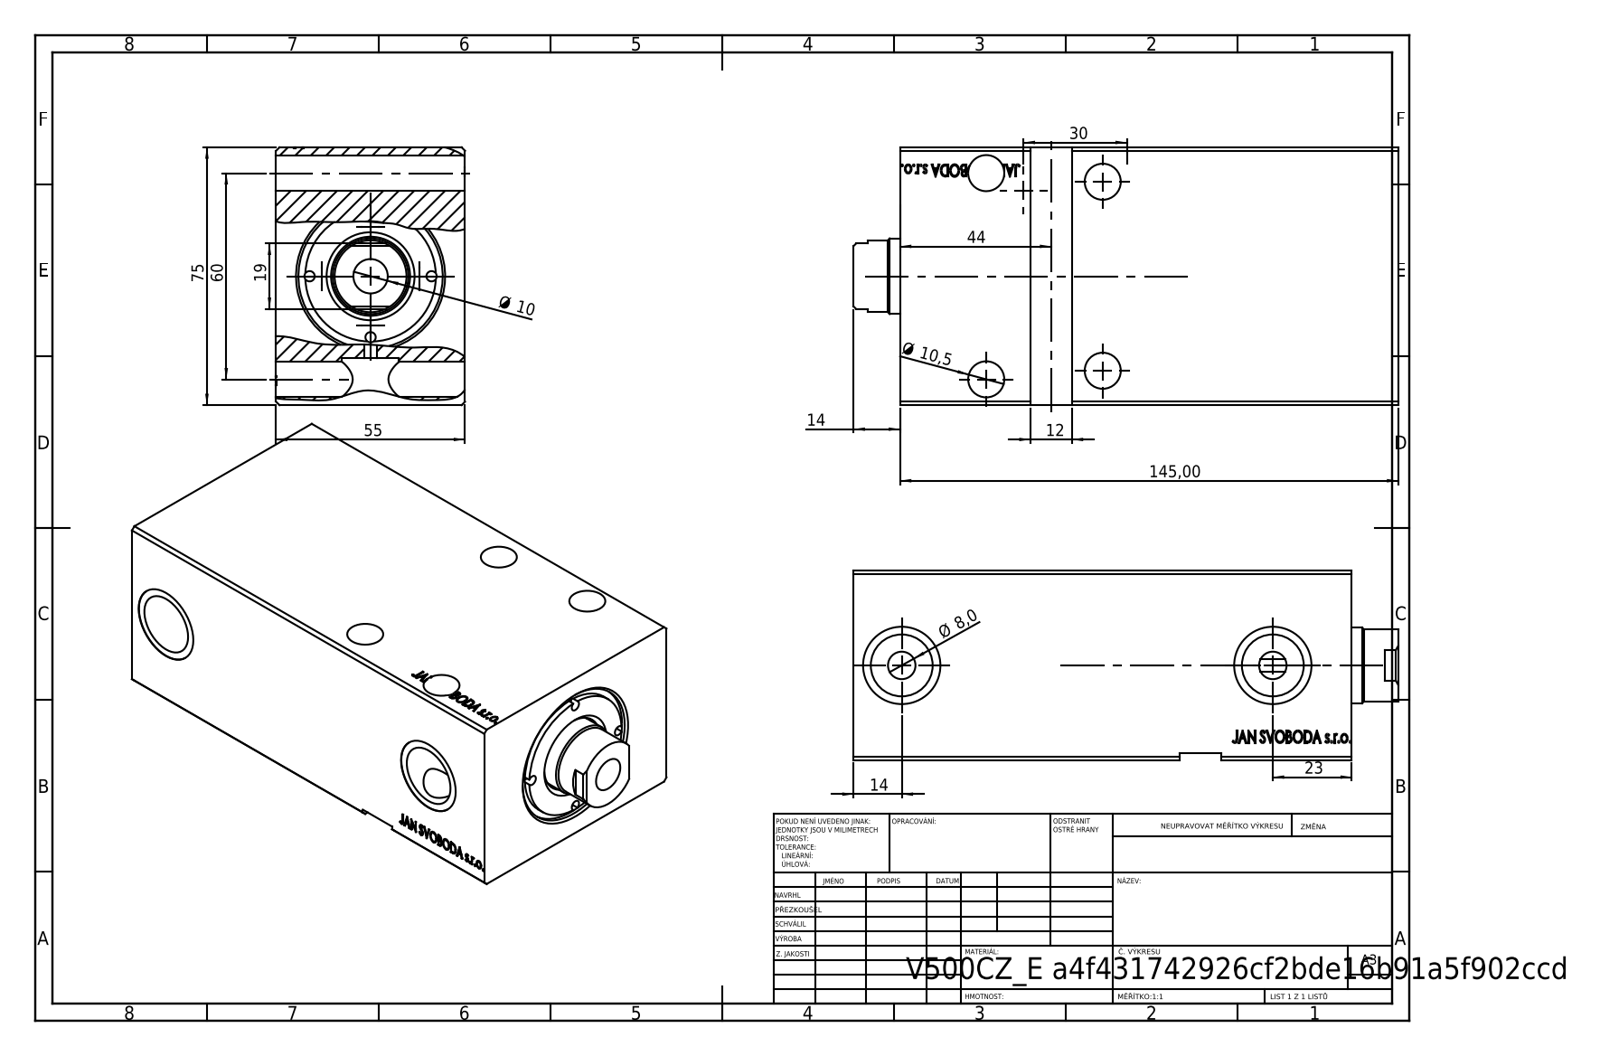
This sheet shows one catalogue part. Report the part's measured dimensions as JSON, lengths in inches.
{"part_name": "V500CZ_VCP_E; V500CZ_VC_vysunovaci_E; V500CZ_E", "step_written_by": "SolidWorks 2019 (CONFIG_CONTROL_DESIGN)", "units": "inches", "bodies": {"solids": 3, "faces": 782, "planar": 376, "cylindrical": 54, "other": 352}, "overall_size": [6.24, 2.953, 2.165], "volume_in3": 32.99, "surface_area_in2": 126.9, "round_holes": [[0.118, 4], [0.413, 4], [0.315, 2], [0.709, 2], [0.886, 2], [0.394, 1], [0.866, 1], [0.906, 1], [1.26, 1], [1.417, 1], [1.654, 1]], "round_bosses_or_shafts": [[1.496, 1], [0.824, 1]], "face_to_face_distances": [2.165, 2.953, 5.709, 4.528, 1.181, 5.701, 1.173, 0.465, 4.063, 5.236], "hole_center_spacings": [0.699, 0.988, 1.339, 1.398, 2.628, 2.165, 2.362, 4.252]}
